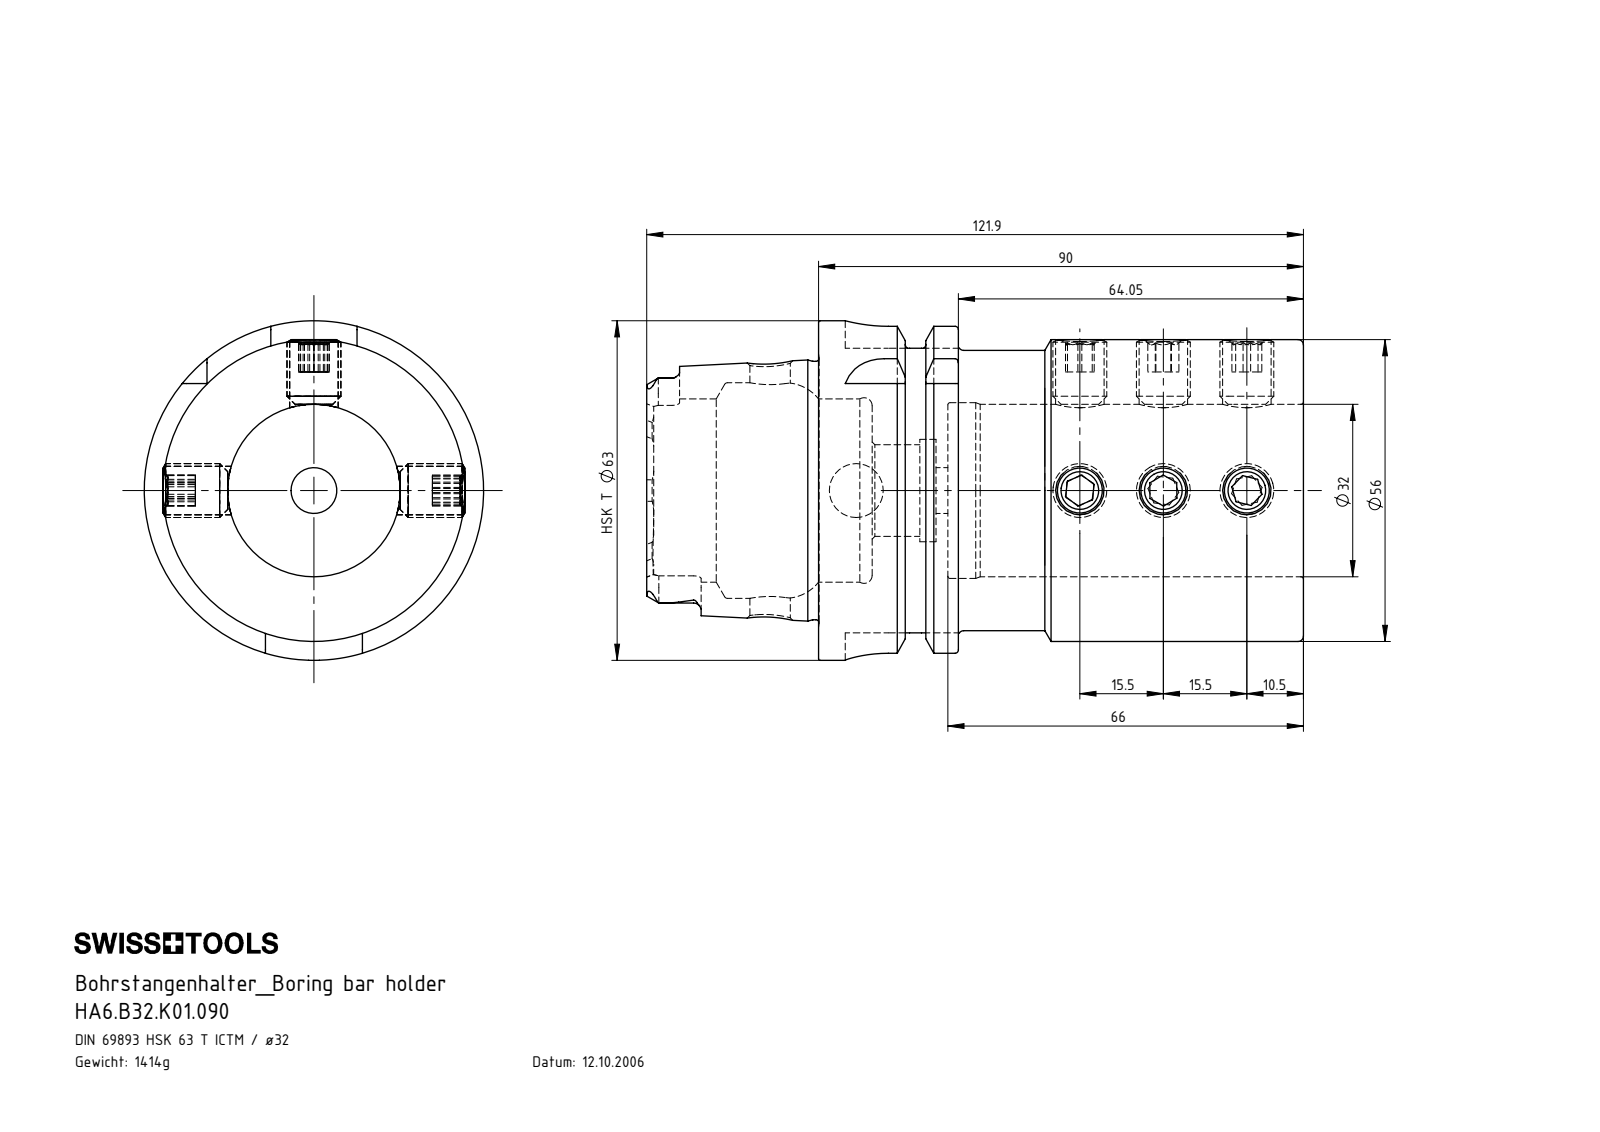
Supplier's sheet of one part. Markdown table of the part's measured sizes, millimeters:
| quantity | value |
| --- | --- |
| part name | HA6.B32.K01.090; HA6-B32.K01.090_B_Fertigbearbeitung; ISO 4026 - M10 x 12 |
| STEP written by | SolidWorks 2017 (AUTOMOTIVE_DESIGN) |
| units | millimeters |
| bodies | 10 solids, 351 faces (129 planar, 87 cylindrical, 135 other) |
| overall size | 121.9 × 63 × 63 |
| volume | 180 178 mm³ |
| surface area | 47 470 mm² |
| round holes (diameter × count) | 9 × 6, 7.5 × 1, 8.5 × 1, 10 × 1, 17 × 1, 19 × 1, 32 × 1, 32.6 × 1, 34 × 1, 40 × 1 |
| round bosses / shafts (diameter × count) | 10 × 6, 63 × 1, 56 × 1, 54.95 × 1, 52 × 1, 47.94 × 1 |
| partial cylindrical surfaces (radius × count) | 1.4 × 6, 2.88 × 4, 8 × 4 |
| main face-to-face distances | 90, 24, 66, 25.95, 1.95, 64.05, 16, 9.95, 14.05, 80.05 |
| hole center spacings | 15.5, 31, 41.5, 57, 57.5, 72.5, 73, 88.5 |
